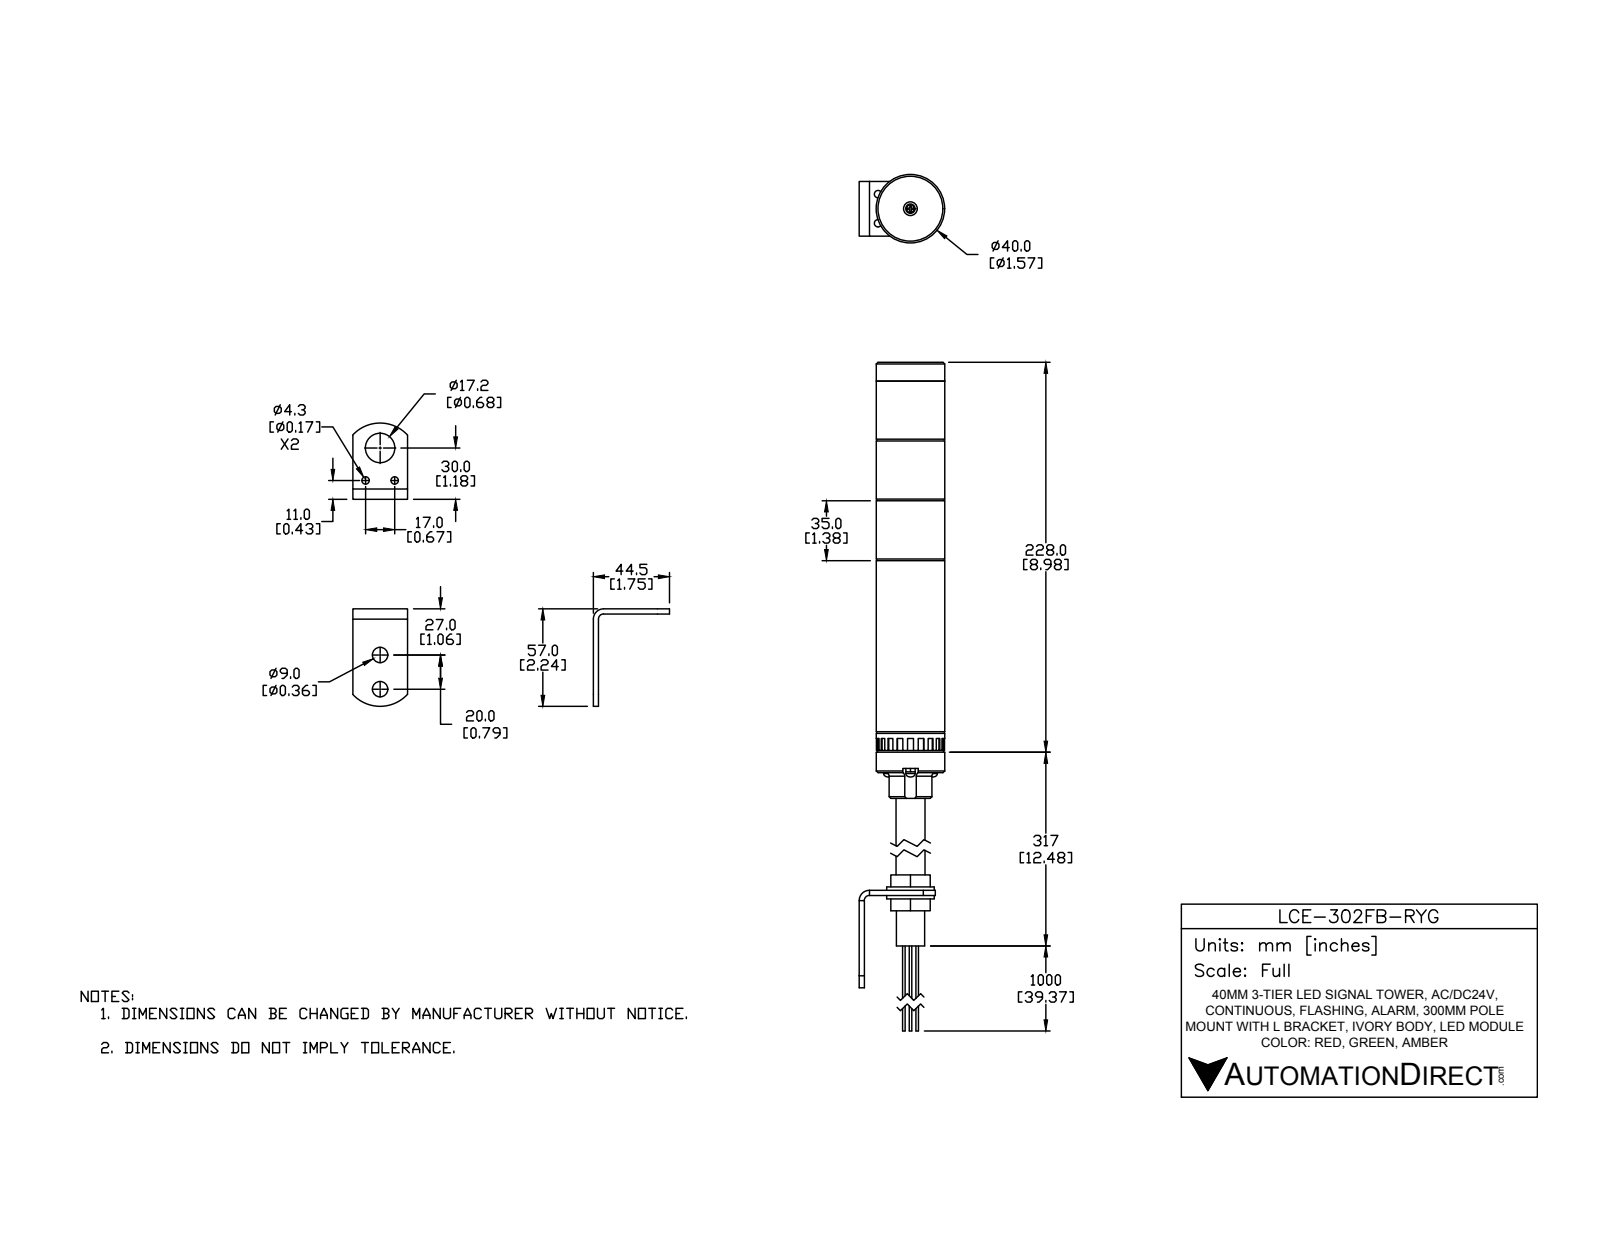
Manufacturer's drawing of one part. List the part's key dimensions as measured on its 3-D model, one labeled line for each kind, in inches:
Part name (STEP PRODUCT): LCE-302FB-RYG
STEP written by: SolidWorks 2016 (AUTOMOTIVE_DESIGN)
Units: inches
Bodies: 35 solids, 385 faces (245 planar, 120 cylindrical, 20 other)
Overall size (bounding box): 24.724 × 1.969 × 1.575
Volume: 21.62 in³ · Surface area: 189.3 in²
Round holes (diameter × count): ⌀0.138 ×3, ⌀0.157 ×3, ⌀0.169 ×2, ⌀0.356 ×2, ⌀0.315 ×1, ⌀0.472 ×1, ⌀0.677 ×1, ⌀0.689 ×1, ⌀0.709 ×1
Round bosses / shafts (diameter × count): ⌀0.059 ×10, ⌀0.217 ×4, ⌀0.118 ×3, ⌀1.575 ×1, ⌀1.555 ×1, ⌀1.516 ×1, ⌀1.094 ×1, ⌀0.669 ×1
Partial cylindrical surfaces — rounded edges, fillets, slot ends (radius × count): R0.177 ×3, R0.858 ×2, R0.118 ×1, R0.236 ×1, R0.492 ×1
Main face-to-face distances: 1.378, 0.039, 2.756, 1.339, 0.433, 1.417, 2.717, 3.976, 5.354, 6.732
Hole centre spacings: 0.591, 1.023, 0.819, 0.24, 0.669, 0.673, 0.787, 0.791
